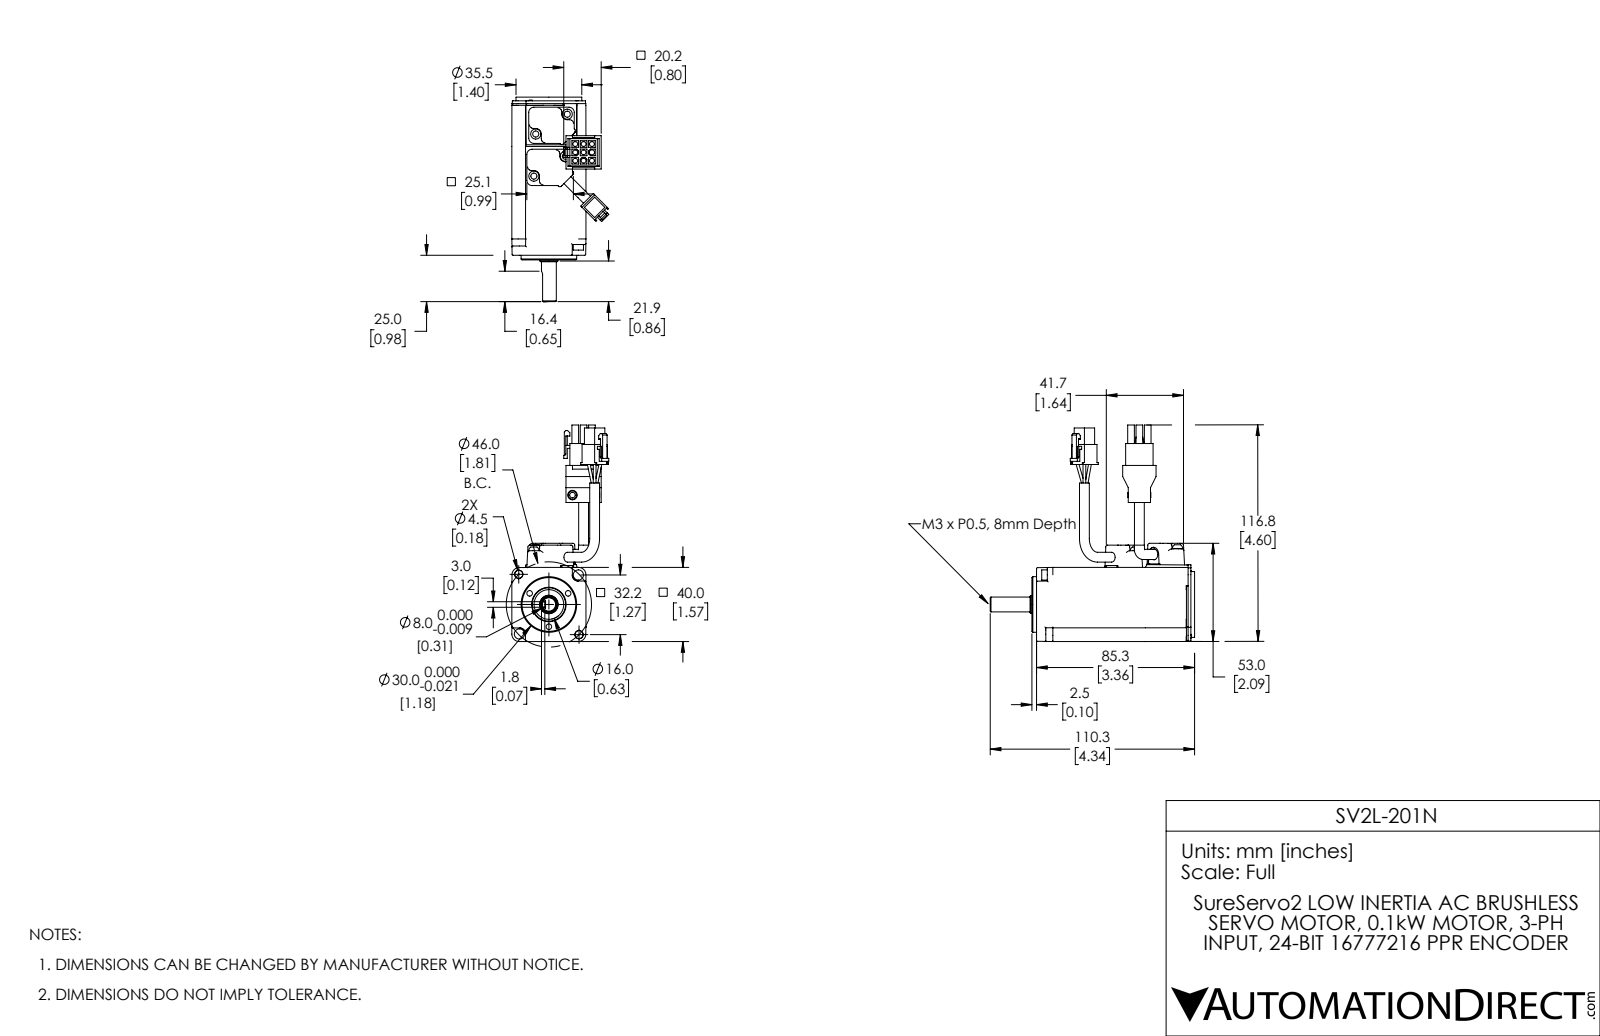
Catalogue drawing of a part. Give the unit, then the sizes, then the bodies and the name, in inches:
Units: inches
Overall size (bounding box): 4.598 × 4.343 × 2.06
Round holes (diameter × count): ⌀0.102 ×8, ⌀0.118 ×3, ⌀0.201 ×2, ⌀0.217 ×2, ⌀0.11 ×1, ⌀0.228 ×1, ⌀0.236 ×1, ⌀0.63 ×1
Round bosses / shafts (diameter × count): ⌀0.059 ×4, ⌀0.209 ×3, ⌀0.217 ×2, ⌀0.181 ×2, ⌀0.098 ×2, ⌀0.079 ×2, ⌀1.398 ×1, ⌀1.181 ×1
Partial cylindrical surfaces — rounded edges, fillets, slot ends (radius × count): R0.02 ×41, R0.039 ×38, R0.079 ×10, R0.11 ×6, R0.024 ×4, R0.039 ×4, R0.157 ×4, R0.03 ×2
Main face-to-face distances: 1.575, 0.142, 0.035, 0.185, 0.177, 0.354, 0.398, 0.043, 0.291, 0.539
Hole centre spacings: 0.177, 0.25, 0.396, 0.354, 0.472, 0.818, 0.501, 0.886
Volume: 9.083 in³ · Surface area: 48.31 in²
Bodies: 1 solid, 806 faces (450 planar, 240 cylindrical, 116 other)
Part name (STEP PRODUCT): ECM-A3H-CX0401RSX 201N r1 surf fill 1b 2B Comb fXT r1b fXT mod heal red1 Coord
STEP written by: SolidWorks 2017 (AUTOMOTIVE_DESIGN)
